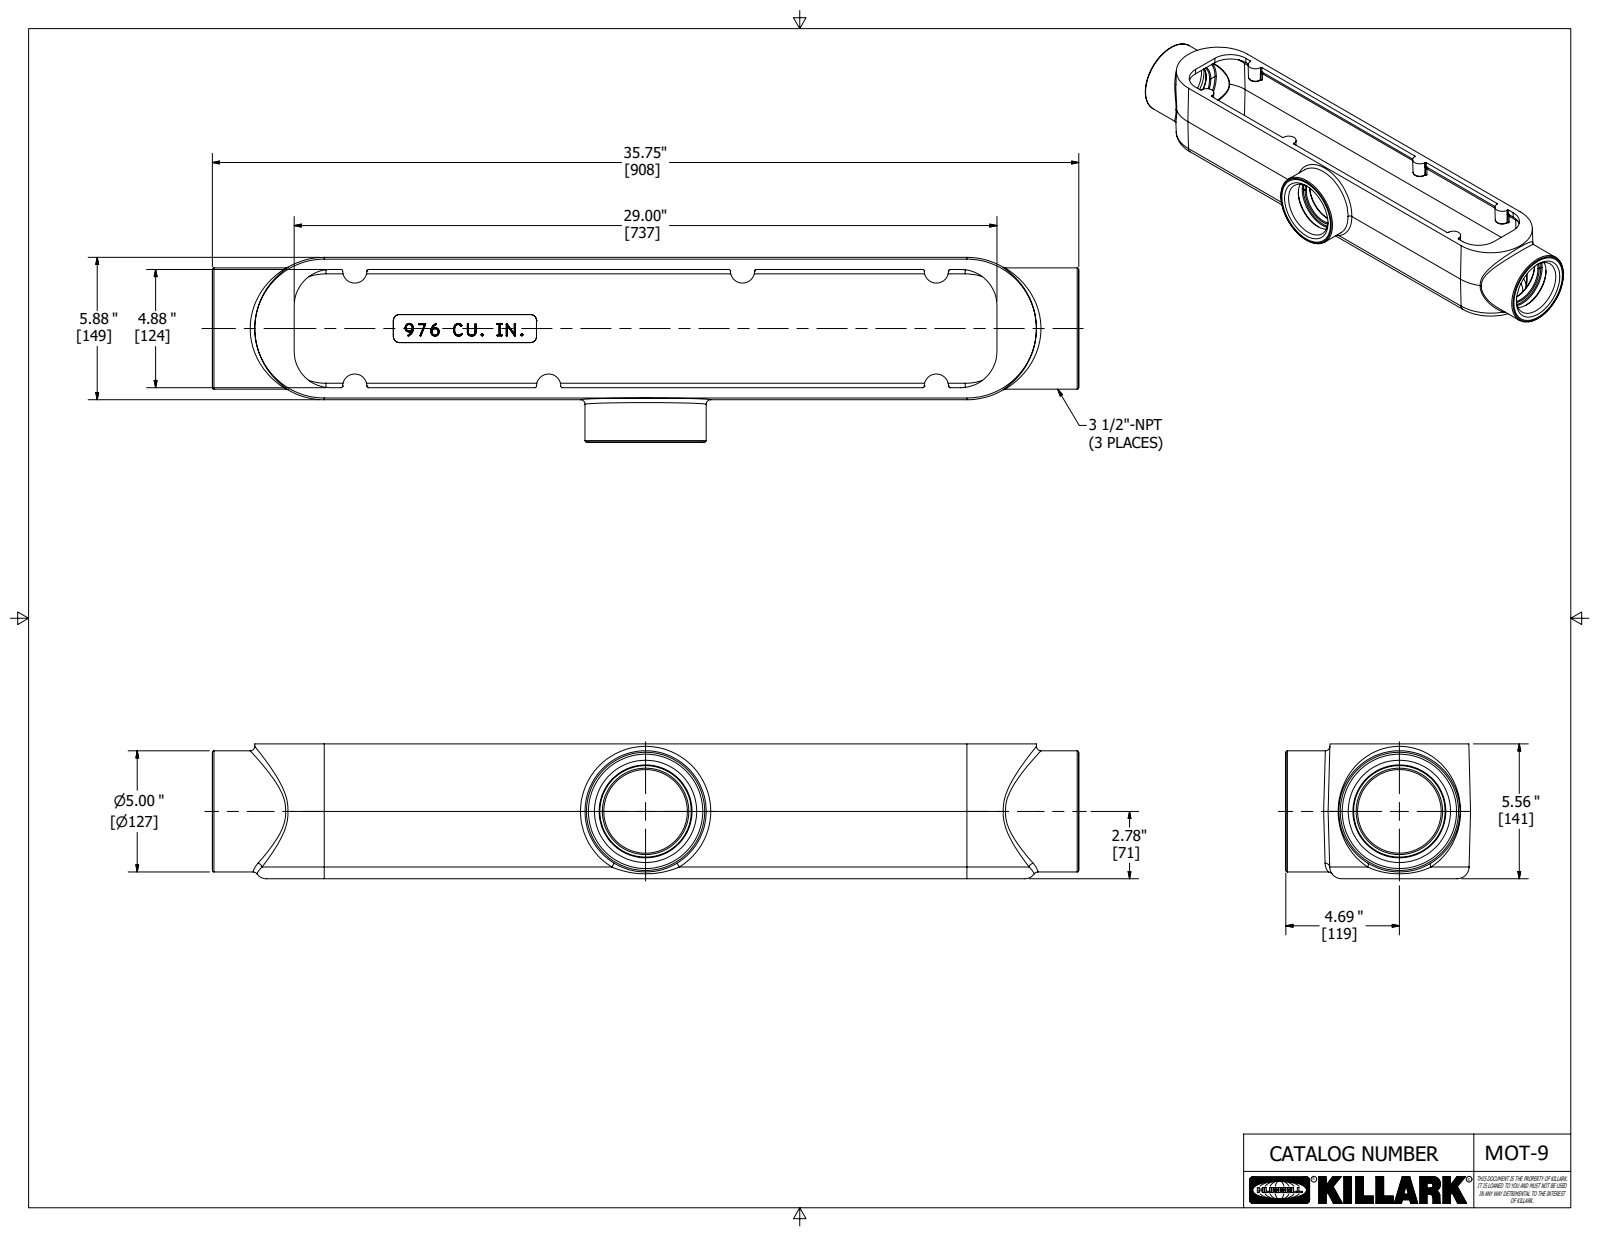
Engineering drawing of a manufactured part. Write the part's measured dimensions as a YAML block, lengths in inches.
part_name: "21317"
step_written_by: "Autodesk Inventor 2020 (AUTOMOTIVE_DESIGN)"
units: inches
bodies: {solids: 1, faces: 653, planar: 271, cylindrical: 71, other: 311}
overall_size: [35.75, 7.625, 5.563]
volume: 243.9
surface_area: 1243
round_holes:
  - {diameter: 3.448, count: 2}
  - {diameter: 4.011, count: 2}
round_bosses_or_shafts:
  - {diameter: 5, count: 2}
partial_cylinders:
  - {radius: 0.062, count: 46}
  - {radius: 0.25, count: 2}
  - {radius: 0.5, count: 2}
  - {radius: 2.25, count: 1}
face_to_face_distances: [0.375, 0.375, 5.875, 5.5, 5.125, 5.5, 5.187, 5.562, 5.447, 5.072]
